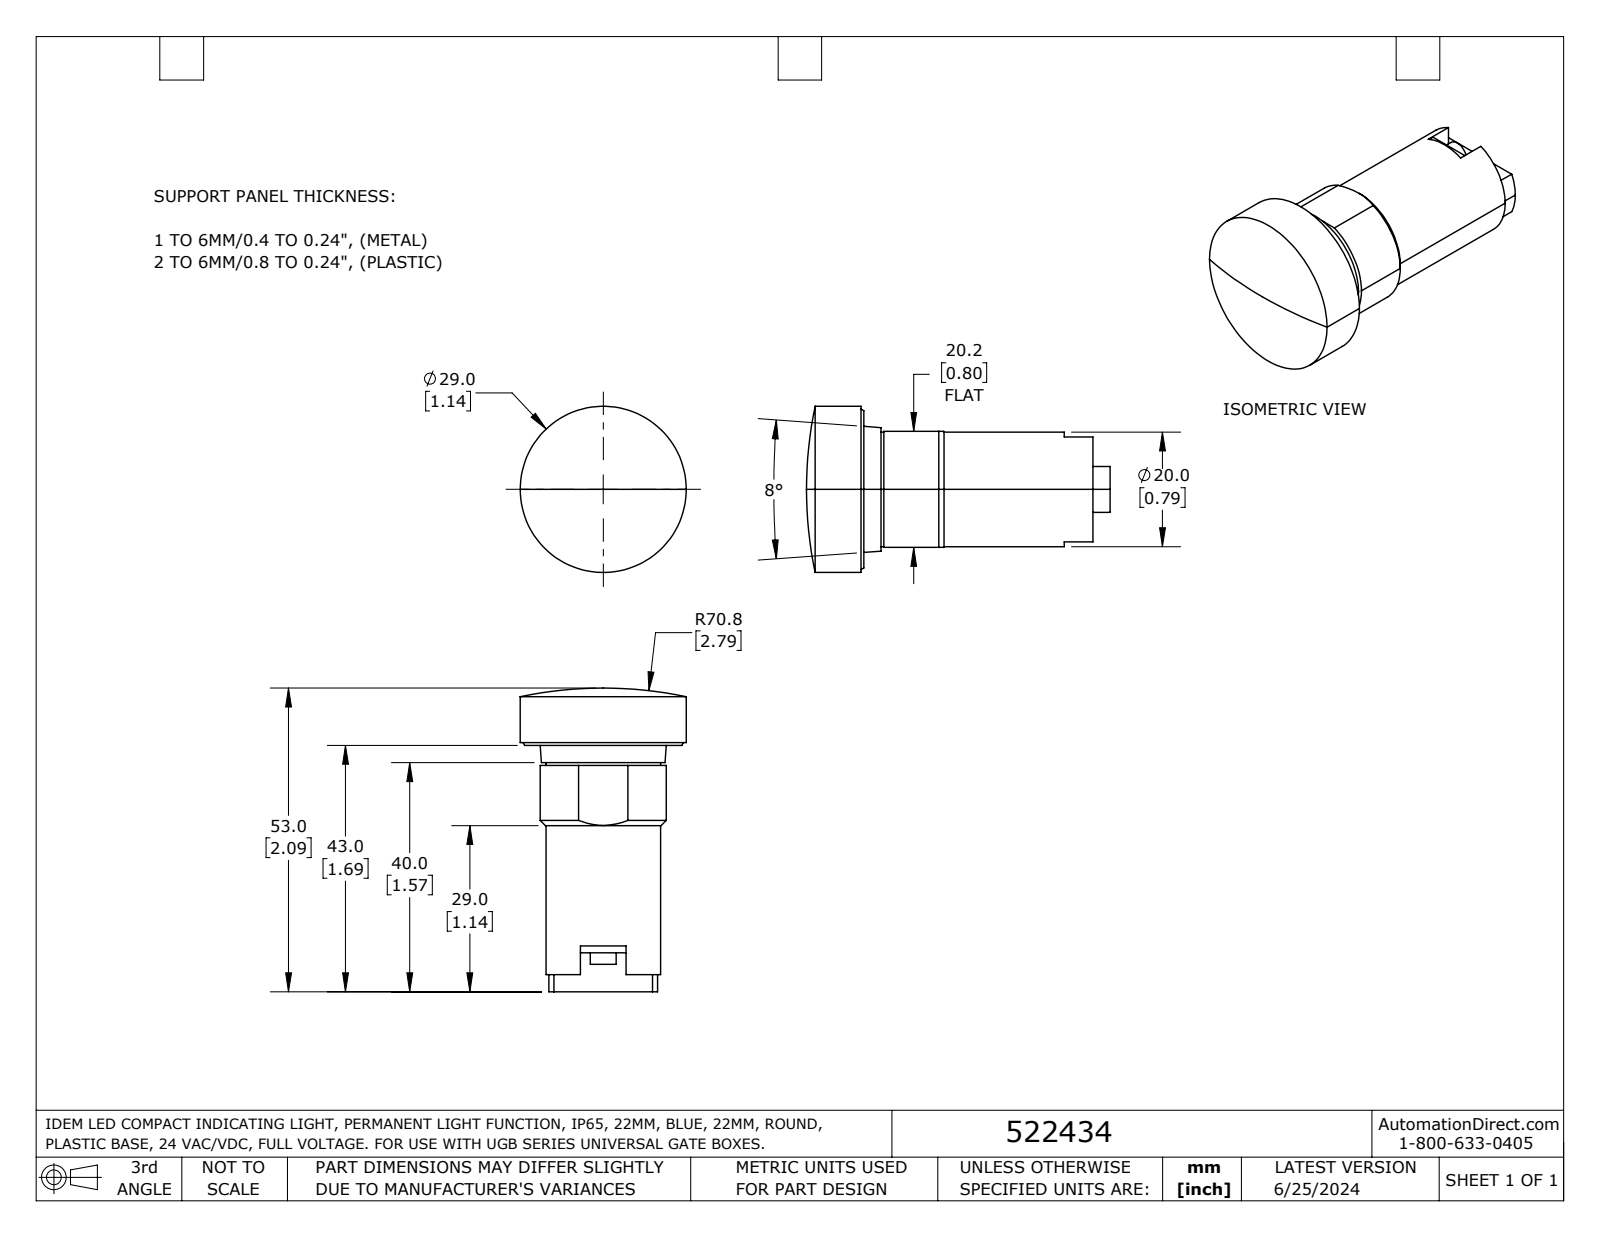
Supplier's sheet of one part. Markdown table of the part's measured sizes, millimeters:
| quantity | value |
| --- | --- |
| part name | 522434 |
| STEP written by | SolidWorks 2023 (AUTOMOTIVE_DESIGN) |
| units | millimeters |
| bodies | 1 solid, 50 faces (24 planar, 18 cylindrical, 8 other) |
| overall size | 53 × 29 × 29 |
| volume | 19 530 mm³ |
| surface area | 5 025 mm² |
| round bosses / shafts (diameter × count) | 4.5 × 2, 29 × 1, 20 × 1 |
| partial cylindrical surfaces (radius × count) | 9.5 × 1, 11 × 1 |
| main face-to-face distances | 6.1, 14.1, 43, 8, 3, 40, 3.5, 0.5, 20.2, 36.5 |
